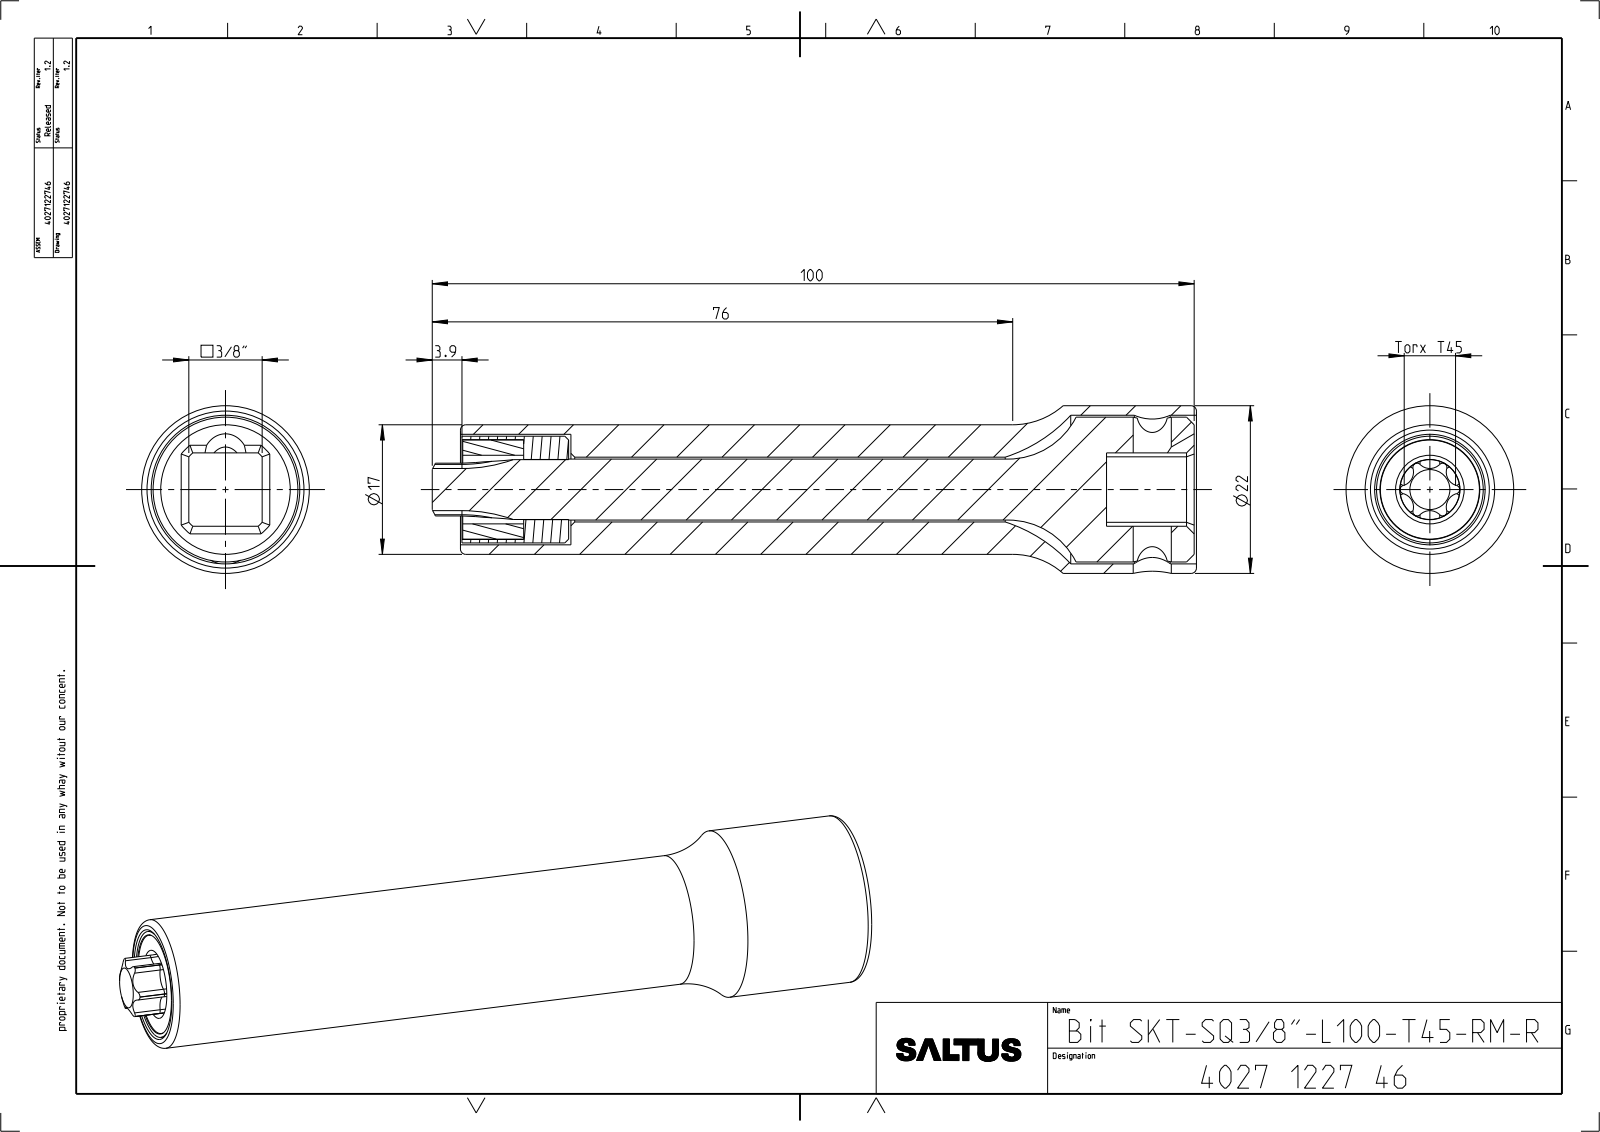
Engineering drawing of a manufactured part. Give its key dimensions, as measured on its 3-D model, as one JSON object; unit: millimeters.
{"part_name": "4027905845; 4027901682; 4027907743; 4027904092_ASM (+2 more)", "step_written_by": "CREO PARAMETRIC BY PTC INC, 2022414 (CONFIG_CONTROL_DESIGN)", "units": "millimeters", "bodies": {"solids": 4, "faces": 135, "planar": 21, "cylindrical": 65, "other": 49}, "overall_size": [100.3, 22, 22], "volume_mm3": 21972, "surface_area_mm2": 15310, "round_holes": [[5, 1], [7.9, 1], [8.5, 1], [9, 1], [13.1, 1], [14.5, 1], [19.5, 1]], "round_bosses_or_shafts": [[22, 1], [19, 1], [17, 1], [14, 1], [13, 1], [8, 1], [7.85, 1]], "partial_cylinders_radius": [[0.54, 12], [1.83, 6], [3, 1], [3.91, 1], [6.45, 1]], "face_to_face_distances": [9.62, 82.1, 14.2, 6.2, 70.3, 76.5, 11.5, 81.8, 88, 70.6]}
